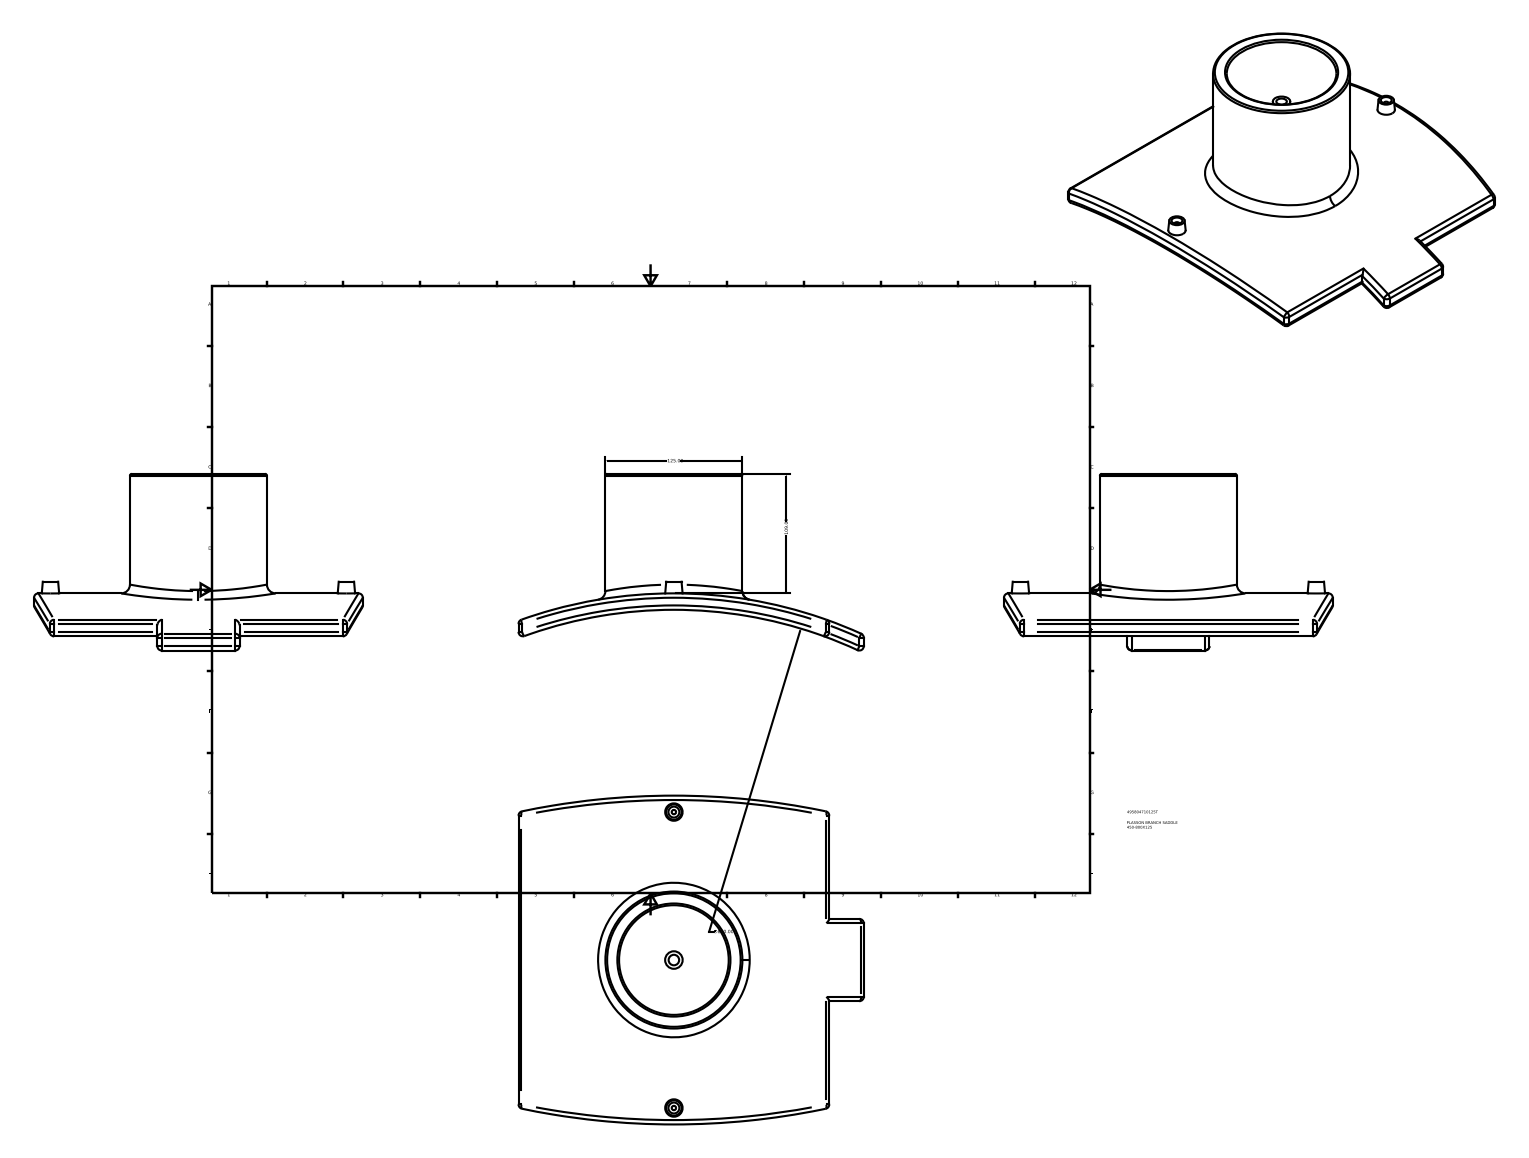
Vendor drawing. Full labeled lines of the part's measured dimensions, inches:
Part name (STEP PRODUCT): 495804710125T
STEP written by: Autodesk Inventor 2015 (AUTOMOTIVE_DESIGN)
Units: inches
Bodies: 1 solid, 66 faces (14 planar, 27 cylindrical, 25 other)
Overall size (bounding box): 12.402 × 11.811 × 6.345
Volume: 109.4 in³ · Surface area: 421.5 in²
Round holes (diameter × count): ⌀0.394 ×2, ⌀0.378 ×1, ⌀3.937 ×1
Round bosses / shafts (diameter × count): ⌀0.157 ×2, ⌀4.921 ×1, ⌀0.63 ×1
Partial cylindrical surfaces — rounded edges, fillets, slot ends (radius × count): R0.157 ×12, R26.664 ×2, R15.748 ×1, R16.339 ×1
Main face-to-face distances: 11.161, 12.402, 1.24, 2.953, 3.874, 0.551, 4.425, 3.138, 2.587, 1.287
Hole centre spacings: 5.315, 10.63
